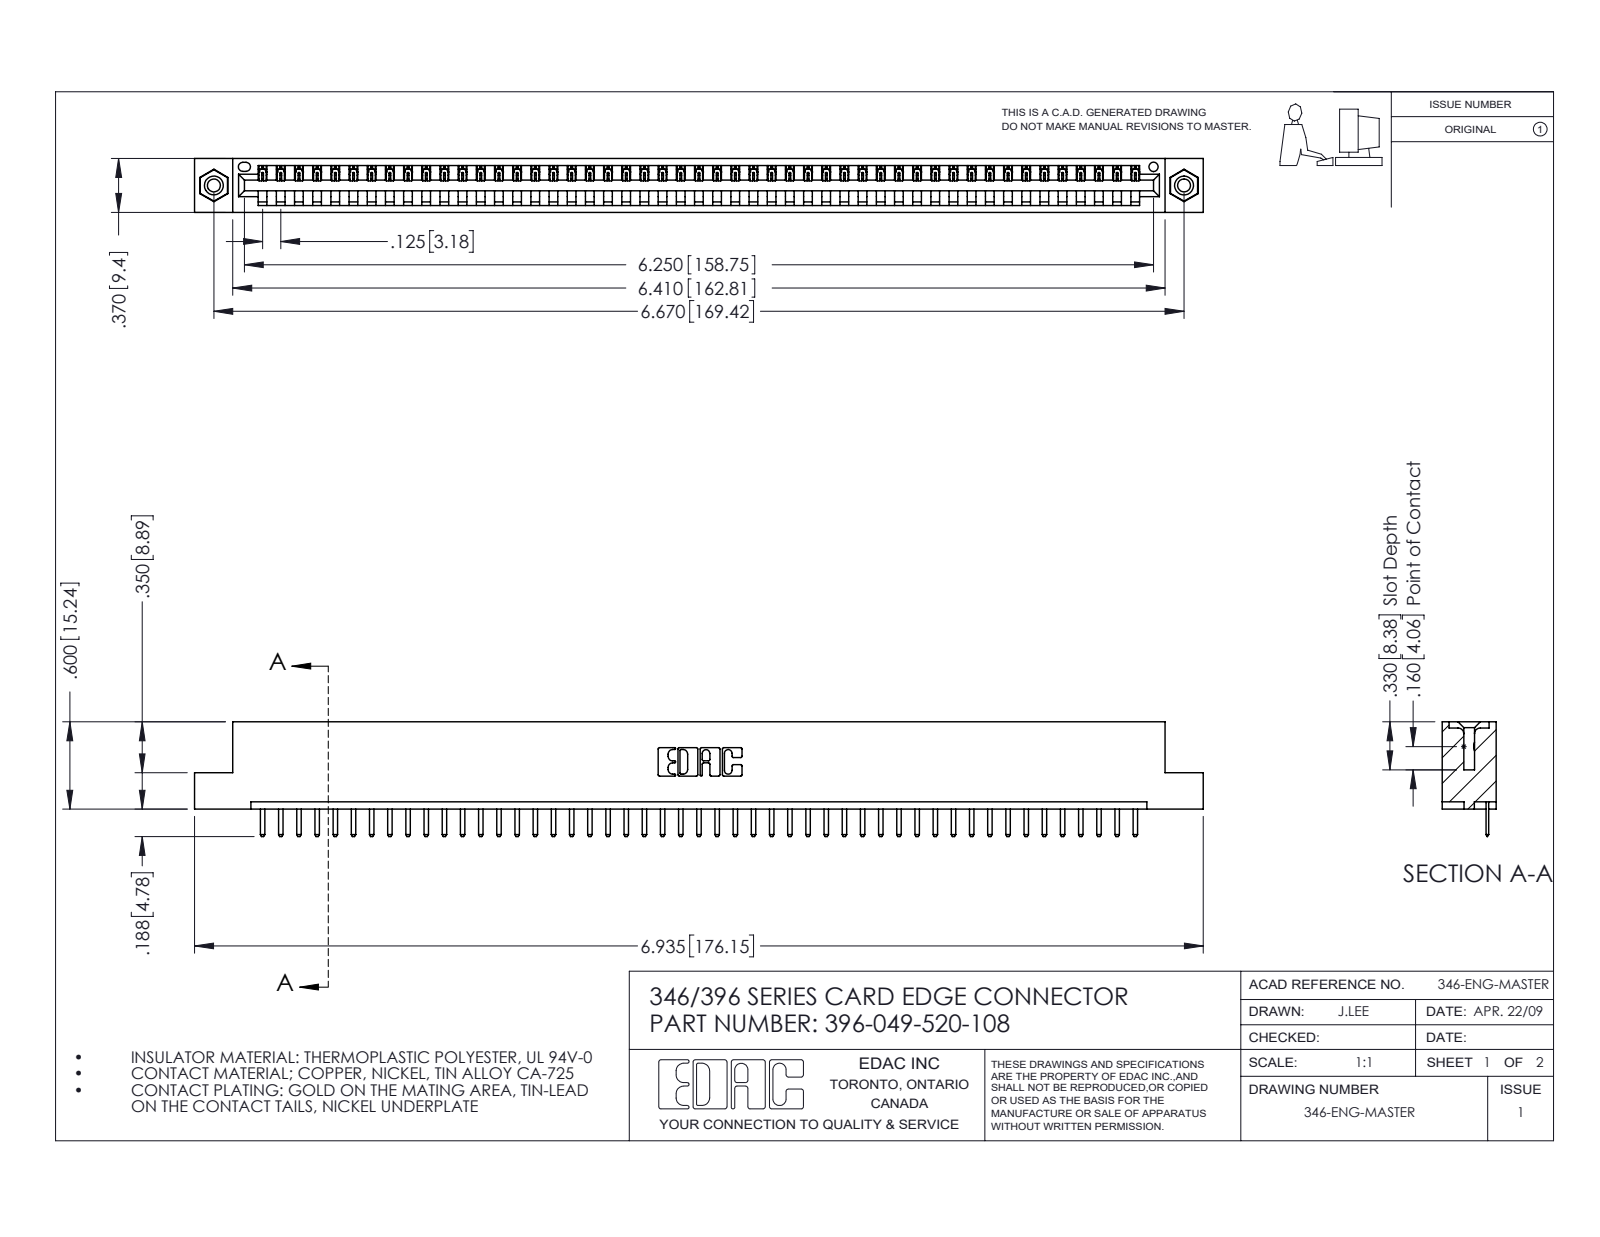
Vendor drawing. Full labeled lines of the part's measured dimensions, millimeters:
Part name (STEP PRODUCT): 396-049-520-108; 345-250-001_345-250-003-102; 345-292-001_345-293-120; 346 Part_Flush Mounting Lugs - 0.156 Dia-TI
STEP written by: SolidWorks 2016 (CONFIG_CONTROL_DESIGN)
Units: millimetres
Bodies: 52 solids, 3220 faces (2166 planar, 1038 cylindrical, 16 other)
Overall size (bounding box): 176.1 × 20 × 9.4
Volume: 16 760 mm³ · Surface area: 20 570 mm²
Round holes (diameter × count): ⌀2.3 ×2, ⌀3.2 ×2, ⌀4 ×2, ⌀1.6 ×1
Round bosses / shafts (diameter × count): ⌀3.9 ×2
Partial cylindrical surfaces — rounded edges, fillets, slot ends (radius × count): R0.3 ×100, R0.2 ×98, R0.3 ×22, R0.2 ×6, R0.8 ×6, R0.7 ×3, R0.8 ×2, R1 ×2
Main face-to-face distances: 1.2, 8.2, 9.4, 6.4, 3.8, 5.6, 2.5, 4.4, 1.8, 7.6
Hole centre spacings: 6.2, 164.1, 169.4
